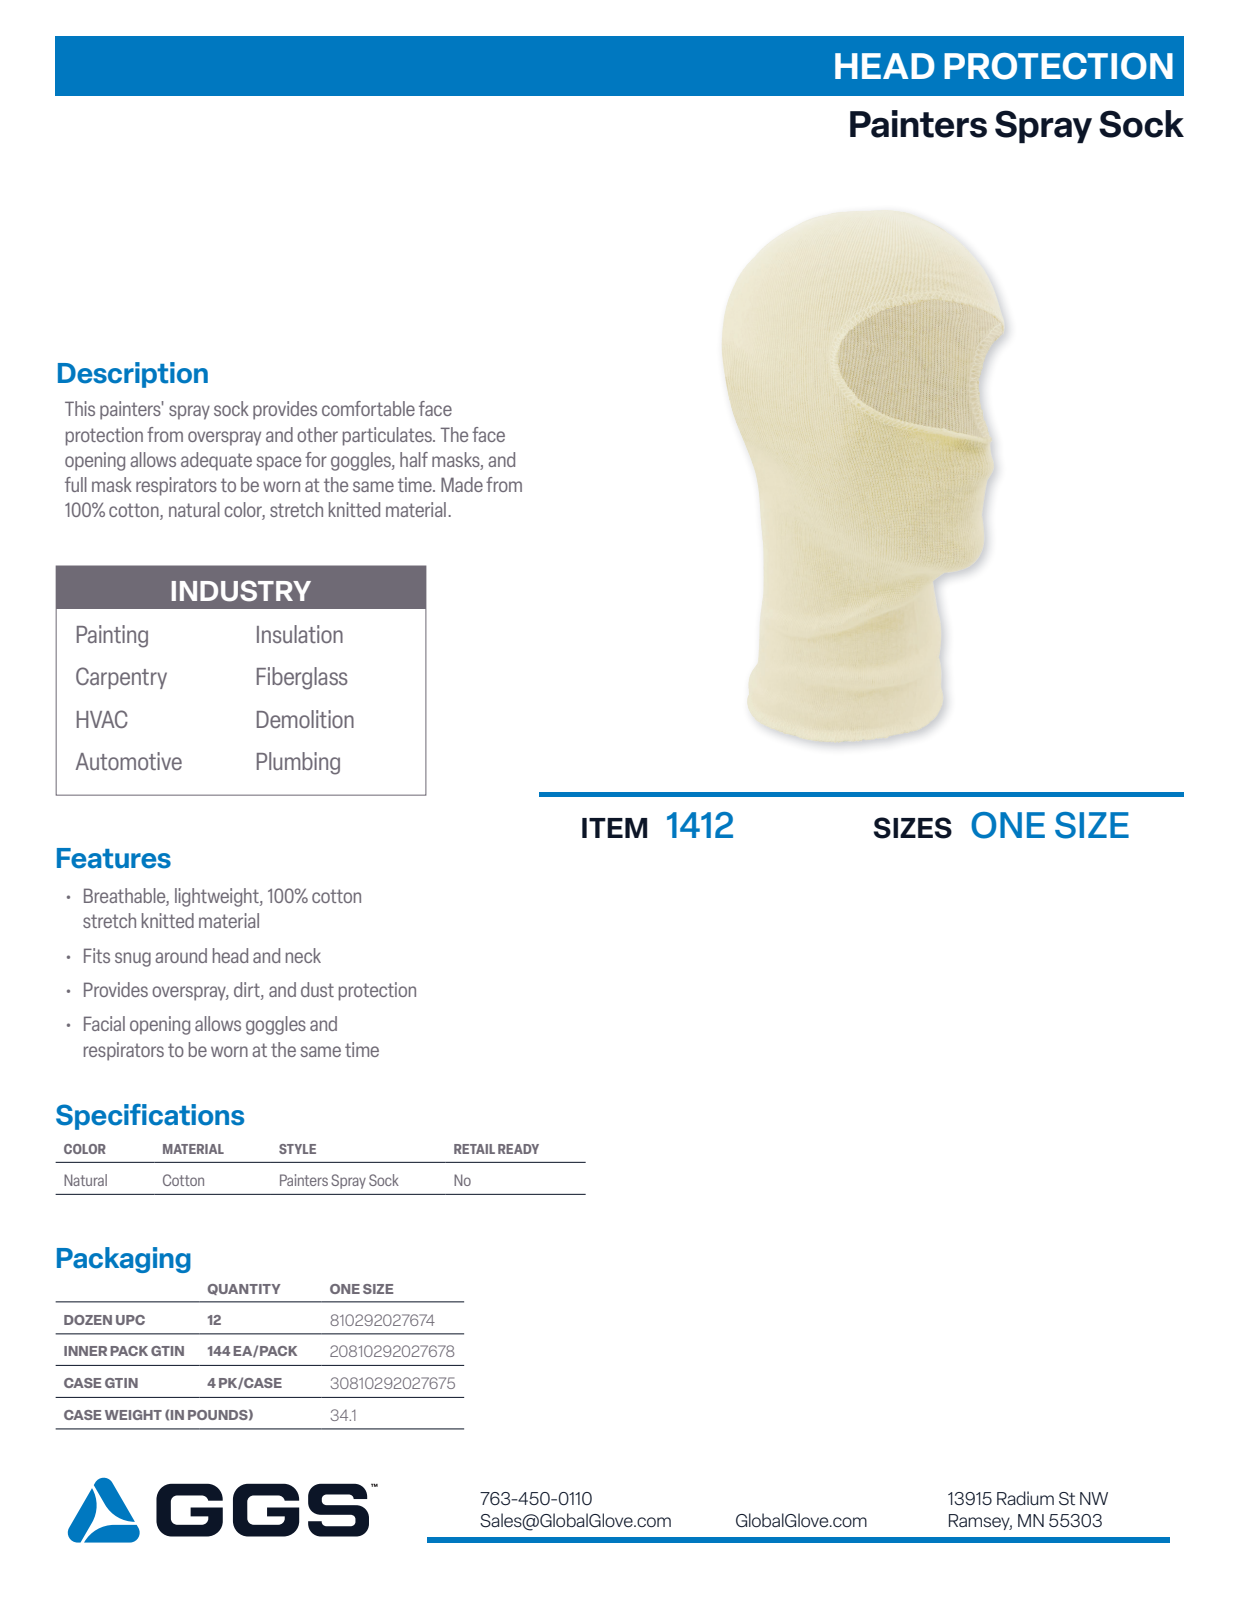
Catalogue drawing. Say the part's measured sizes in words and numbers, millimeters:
Its 3-D file was written by "ACIS (automotive_design)". It is 2 solids with 35 faces: 9 planar, 16 cylindrical and 10 other. Overall it measures 105 by 20 by 20 millimeters. Its volume is 23 479 cubic millimeters and its surface area 10 134 square millimeters. Round holes: 1 of diameter 16.54. Round bosses or shafts: 1 of diameter 20, 1 of diameter 15. Partial cylindrical surfaces (rounded edges, fillets, slot ends): 1 of radius 1.08, 1 of radius 1.77, 1 of radius 2.44, 1 of radius 7.49. The main face-to-face distances are 37, 105, 68, 0.7, 76.52, 39.52, 28.48.
